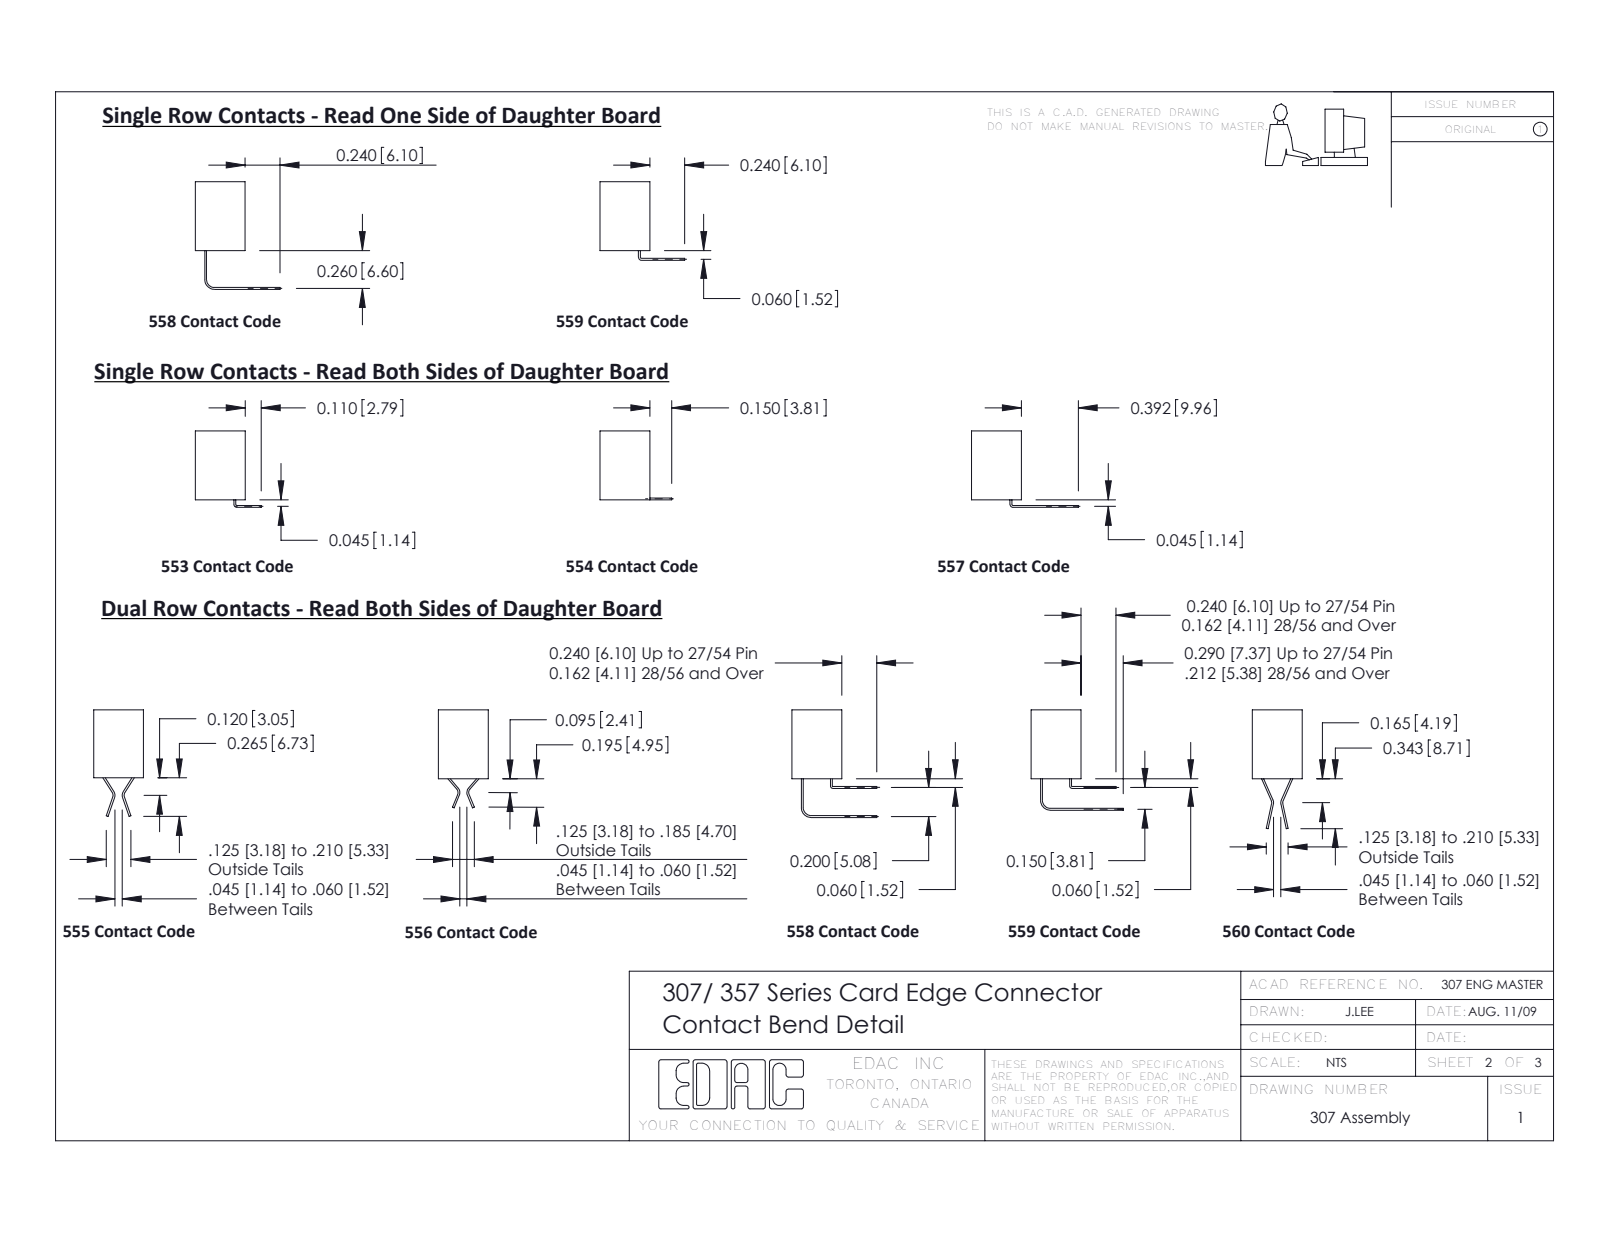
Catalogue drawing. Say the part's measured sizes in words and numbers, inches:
The part is named "307 Part_.156 Dia Mounting Holes; 357-088-559-208; 345-250-001_345-250-003-102; 307-290-001_559 - 2 (Single) (+1 more)". Its 3-D file was written by "SolidWorks 2020 (CONFIG_CONTROL_DESIGN)". It is 91 solids with 4623 faces: 3006 planar, 1511 cylindrical and 106 other. Overall it measures 7.77 by 0.711 by 0.689 inches. Its volume is 1.301 cubic inches and its surface area 43.46 square inches. Round holes: 2 of diameter 0.089, 2 of diameter 0.125, 2 of diameter 0.156. Round bosses or shafts: 2 of diameter 0.155. Partial cylindrical surfaces (rounded edges, fillets, slot ends): 227 of radius 0.02, 88 of radius 0.023, 22 of radius 0.01, 6 of radius 0.007, 6 of radius 0.031, 3 of radius 0.026, 2 of radius 0.012, 2 of radius 0.025. The main face-to-face distances are 0.357, 0.2, 0.014, 0.143, 0.357, 0.143, 0.214, 0.5, 0.157, 0.343. The hole center spacings are 7.46.
